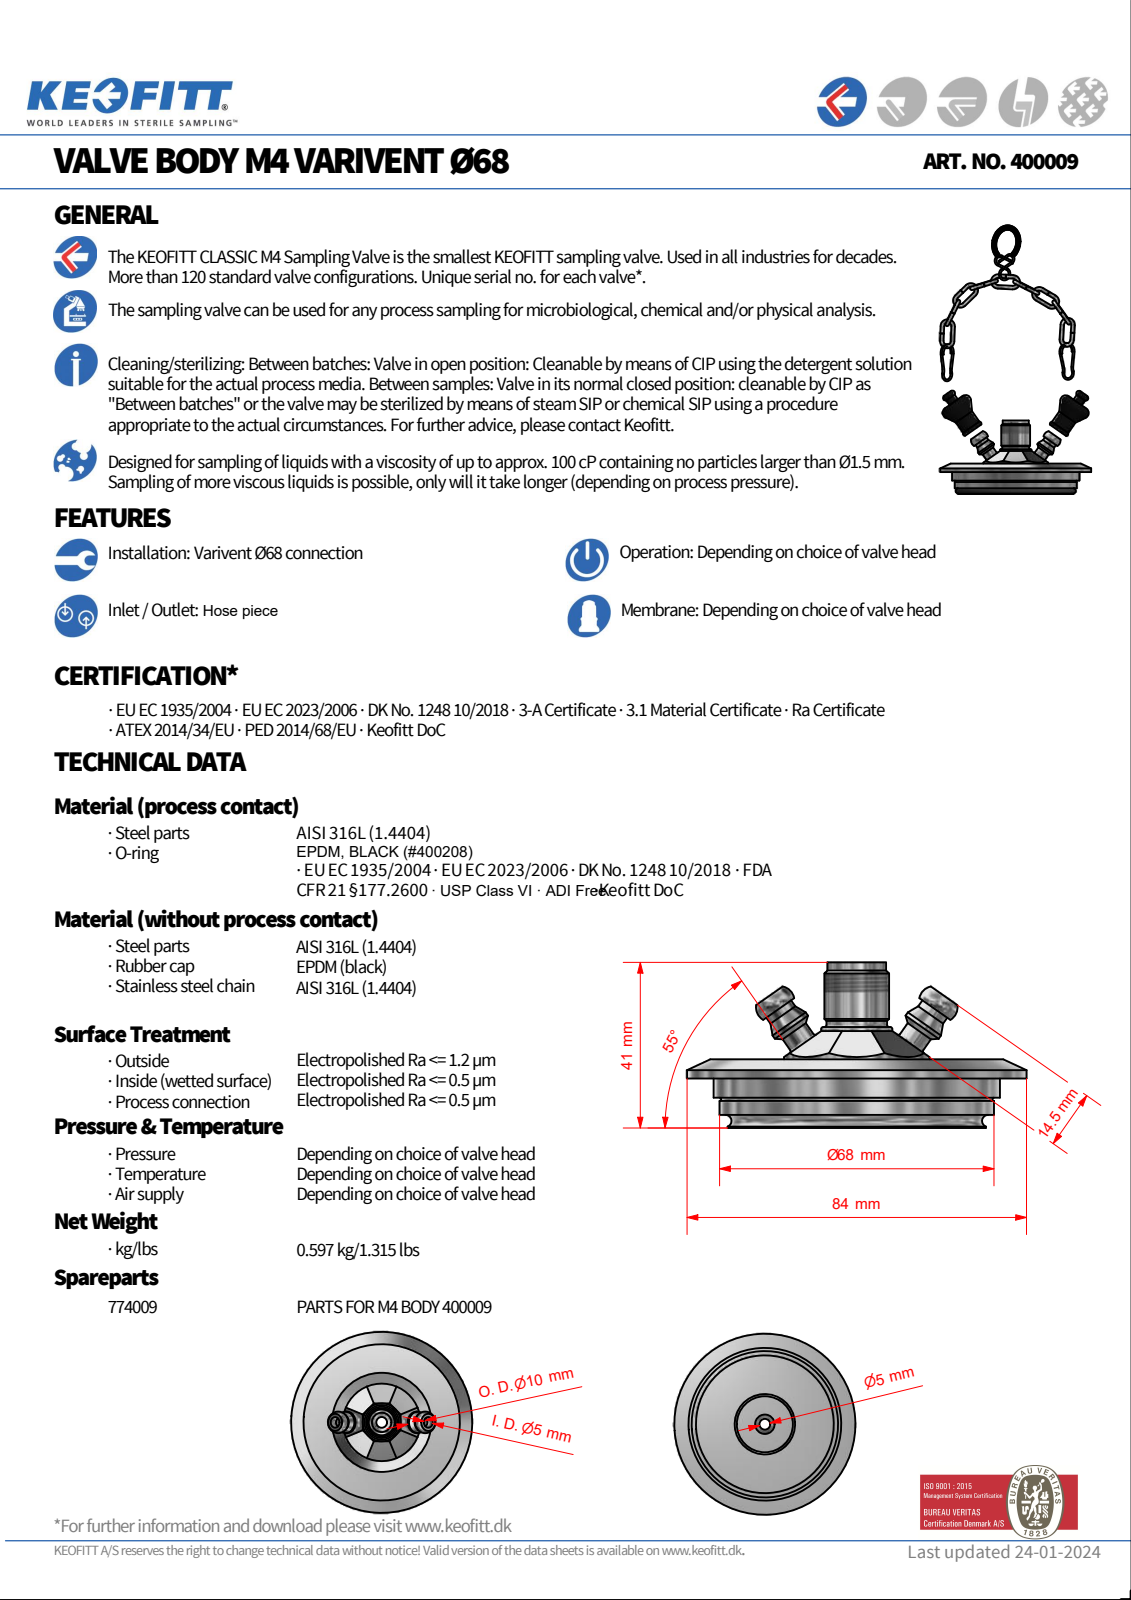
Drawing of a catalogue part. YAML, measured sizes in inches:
step_written_by: "Autodesk Inventor 2008 (AUTOMOTIVE_DESIGN)"
units: inches
bodies: {solids: 96, faces: 360, planar: 99, cylindrical: 84, other: 177}
overall_size: [5.626, 3.307, 3.307]
volume: 5.173
surface_area: 35.65
round_holes:
  - {diameter: 0.079, count: 9}
  - {diameter: 0.138, count: 2}
  - {diameter: 0.52, count: 1}
round_bosses_or_shafts:
  - {diameter: 0.079, count: 21}
  - {diameter: 0.433, count: 2}
  - {diameter: 0.394, count: 2}
  - {diameter: 0.276, count: 2}
  - {diameter: 0.256, count: 2}
  - {diameter: 0.22, count: 2}
  - {diameter: 0.197, count: 2}
  - {diameter: 0.157, count: 2}
partial_cylinders:
  - {radius: 0.004, count: 9}
face_to_face_distances: [0.669, 0.472, 0.197, 0.024, 0.449, 0.646, 0.138, 0.114, 0.335, 0.531]
